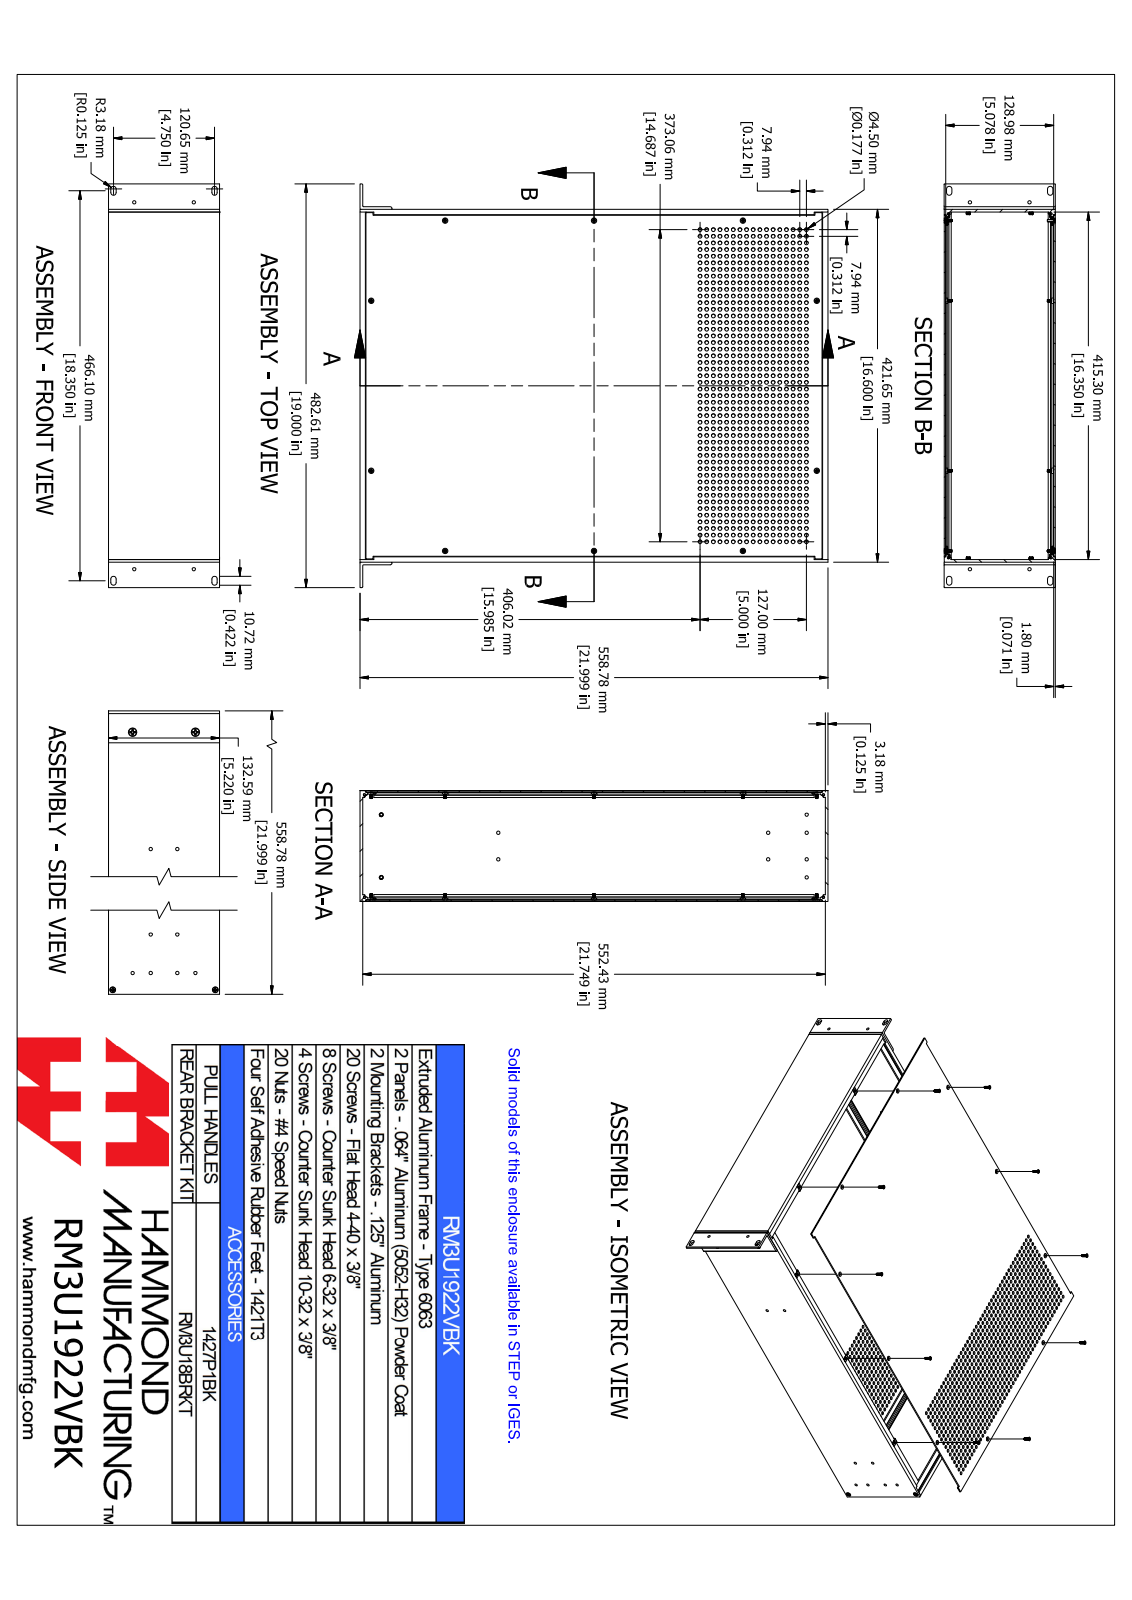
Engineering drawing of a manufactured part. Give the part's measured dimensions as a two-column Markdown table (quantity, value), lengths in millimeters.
| quantity | value |
| --- | --- |
| part name | RM3U1922VBK |
| STEP written by | SolidWorks 2021 (AUTOMOTIVE_DESIGN) |
| units | millimeters |
| bodies | 60 solids, 3916 faces (952 planar, 2176 cylindrical, 788 other) |
| overall size | 560.4 × 482.6 × 132.6 |
| volume | 1 789 000 mm³ |
| surface area | 1 583 000 mm² |
| round holes (diameter × count) | 4.5 × 1632, 4 × 10, 4.1 × 10, 4 × 6, 4.2 × 6, 3.5 × 4, 4 × 4, 4 × 4, 4.3 × 4, 5 × 2 |
| round bosses / shafts (diameter × count) | 5.1 × 10, 2.8 × 10, 6 × 6, 3.5 × 6, 9.1 × 2, 4.8 × 2 |
| partial cylindrical surfaces (radius × count) | 0.3 × 80, 0.6 × 80, 0.2 × 40, 0.4 × 40, 0.4 × 16, 1 × 16, 1 × 14, 0.9 × 9 |
| main face-to-face distances | 130.8, 1.8, 132.6, 129, 418.5, 3.2, 3.2, 555.6, 421.7, 415.3 |
| hole center spacings | 31.8, 130.2, 177.8, 8, 203.2, 23.8, 15.9, 39.7 |
